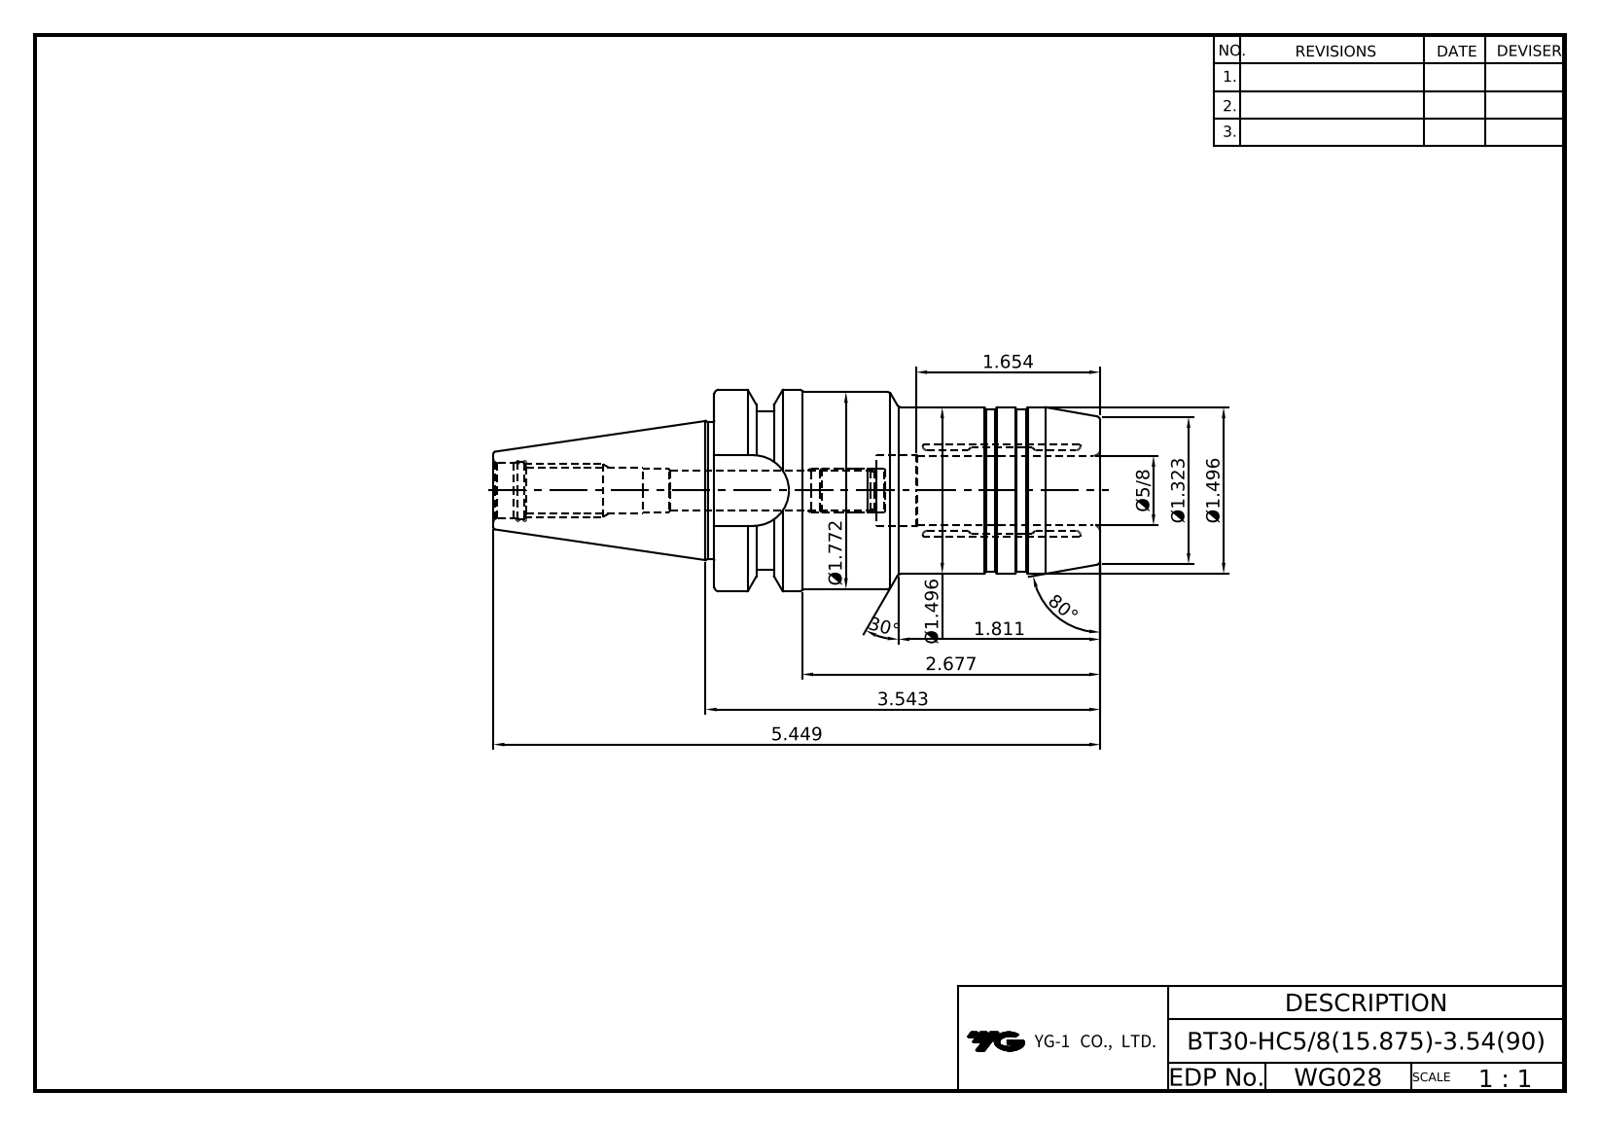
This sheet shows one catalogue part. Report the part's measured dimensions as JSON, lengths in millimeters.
{"part_name": "LO-BT30ADB-HC15.875-90", "step_written_by": "Autodesk Inventor 2020 (AUTOMOTIVE_DESIGN)", "units": "millimeters", "bodies": {"solids": 1, "faces": 96, "planar": 20, "cylindrical": 39, "other": 37}, "overall_size": [138.4, 46, 46], "volume_mm3": 120442, "surface_area_mm2": 23960, "round_holes": [[3.24, 4], [4, 4], [8.92, 1], [10, 1], [10.11, 1], [12.5, 1], [13.1, 1], [15.88, 1], [16.4, 1]], "round_bosses_or_shafts": [[46, 1], [45, 1], [38, 1], [37, 1], [31.2, 1]], "partial_cylinders_radius": [[8.05, 1], [18, 1]], "face_to_face_distances": [88, 32.6, 13.6, 74.4, 37, 23.4, 51, 9.6, 4, 27.4]}
